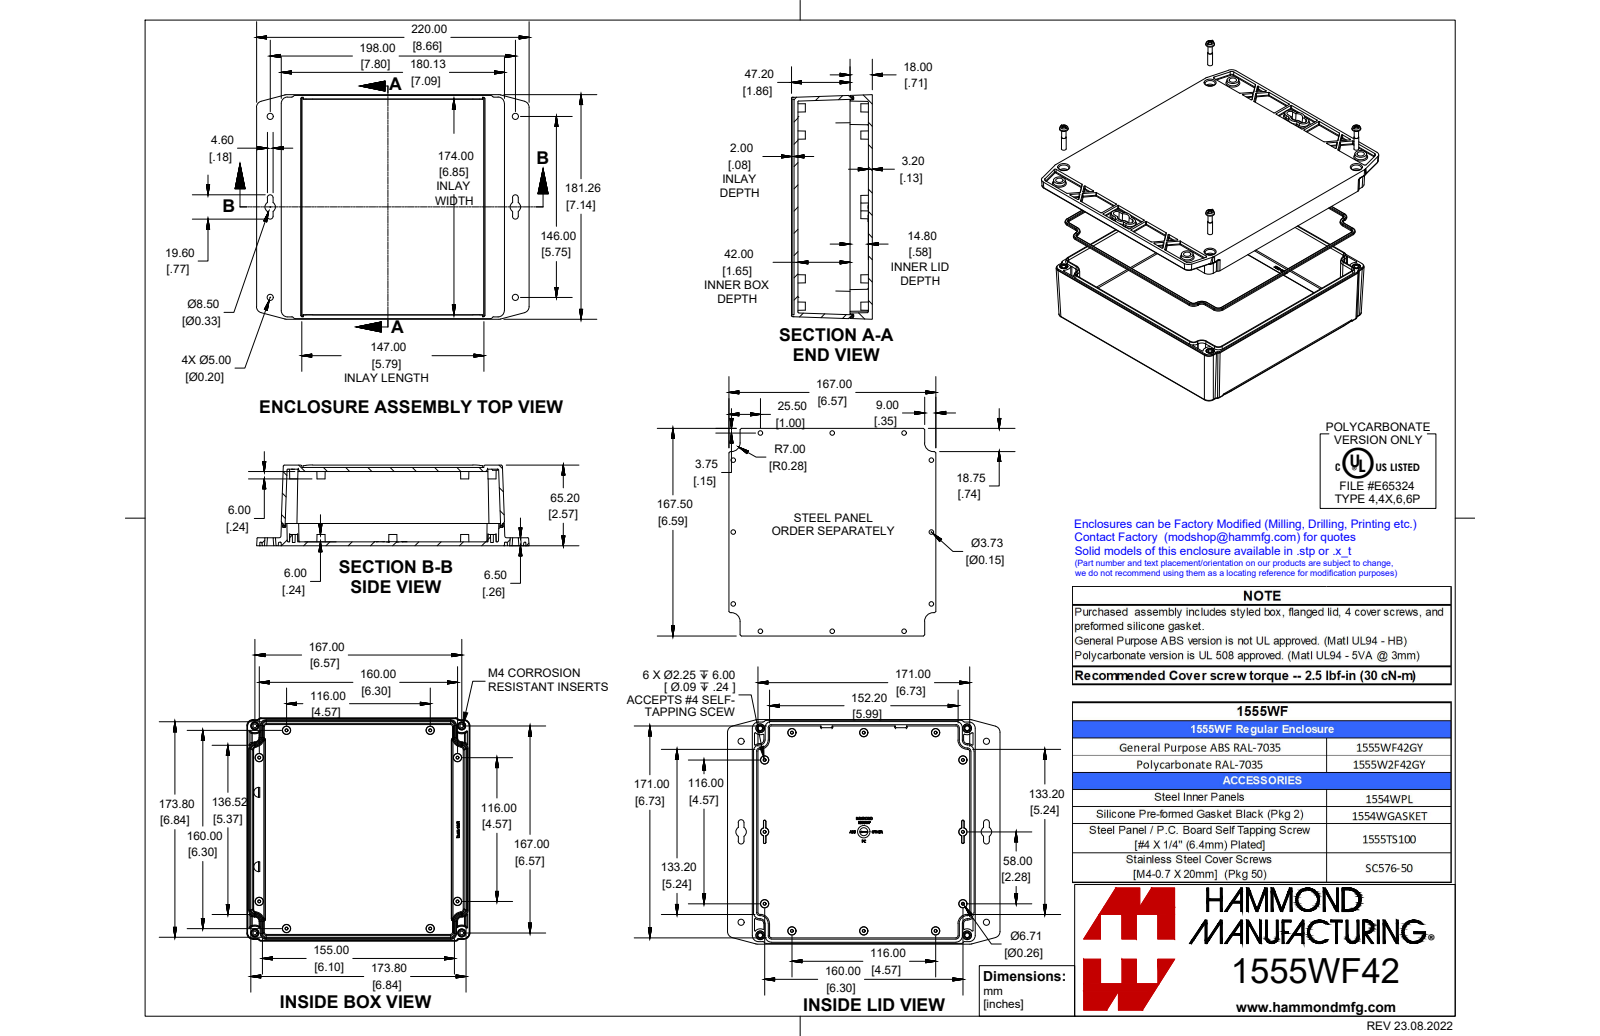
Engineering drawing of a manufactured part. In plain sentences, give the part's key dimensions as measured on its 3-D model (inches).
The part is named "1555WF42GY". Its 3-D file was written by "SolidWorks 2021 (AUTOMOTIVE_DESIGN)". It is 7 solids with 1436 faces: 472 planar, 348 cylindrical and 616 other. Overall it measures 8.661 by 7.141 by 2.641 inches. Its volume is 24.52 cubic inches and its surface area 399.5 square inches. Round holes: 4 of diameter 0.128, 4 of diameter 0.158. Round bosses or shafts: 4 of diameter 0.276, 4 of diameter 0.153, 4 of diameter 0.138, 1 of diameter 0.466. Partial cylindrical surfaces (rounded edges, fillets, slot ends): 130 of radius 0.02, 45 of radius 0.031, 16 of radius 0.012, 8 of radius 0.039, 8 of radius 0.104, 8 of radius 0.197, 8 of radius 0.199, 4 of radius 0.118. The main face-to-face distances are 0.126, 2.362, 2.488, 2.236, 0.122, 0.13, 2.311, 0.118, 0.256, 2.232. The hole center spacings are 6.575, 9.298.
